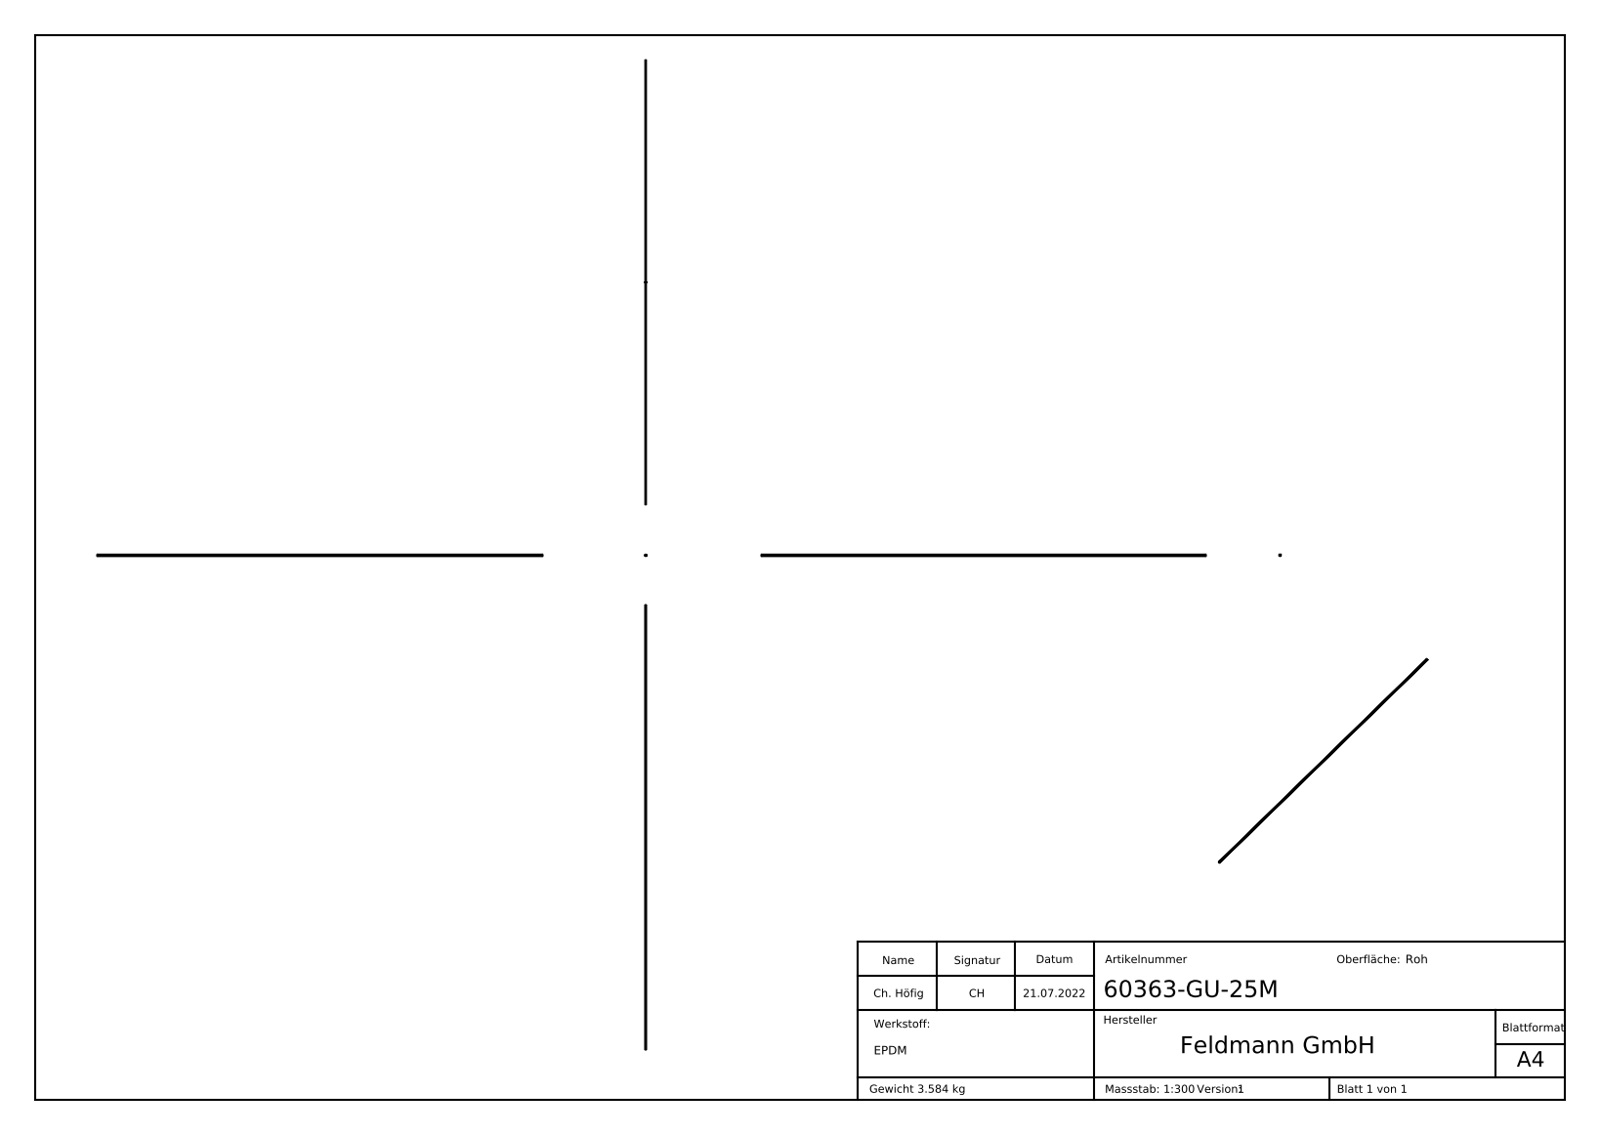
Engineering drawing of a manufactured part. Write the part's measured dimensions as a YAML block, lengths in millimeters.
part_name: "60363-GU-25M"
step_written_by: "SolidWorks 2018 (CONFIG_CONTROL_DESIGN)"
units: millimeters
bodies: {solids: 1, faces: 391, planar: 198, cylindrical: 40, other: 153}
overall_size: [25000, 25.2, 23]
volume: 3035000
surface_area: 4187000
partial_cylinders:
  - {radius: 0.4, count: 22}
  - {radius: 0.3, count: 14}
  - {radius: 1, count: 2}
  - {radius: 1.5, count: 2}
face_to_face_distances: [1.3, 23.1, 1.5, 3.5, 21.8, 24.4, 5, 2, 1.56, 1.55]
